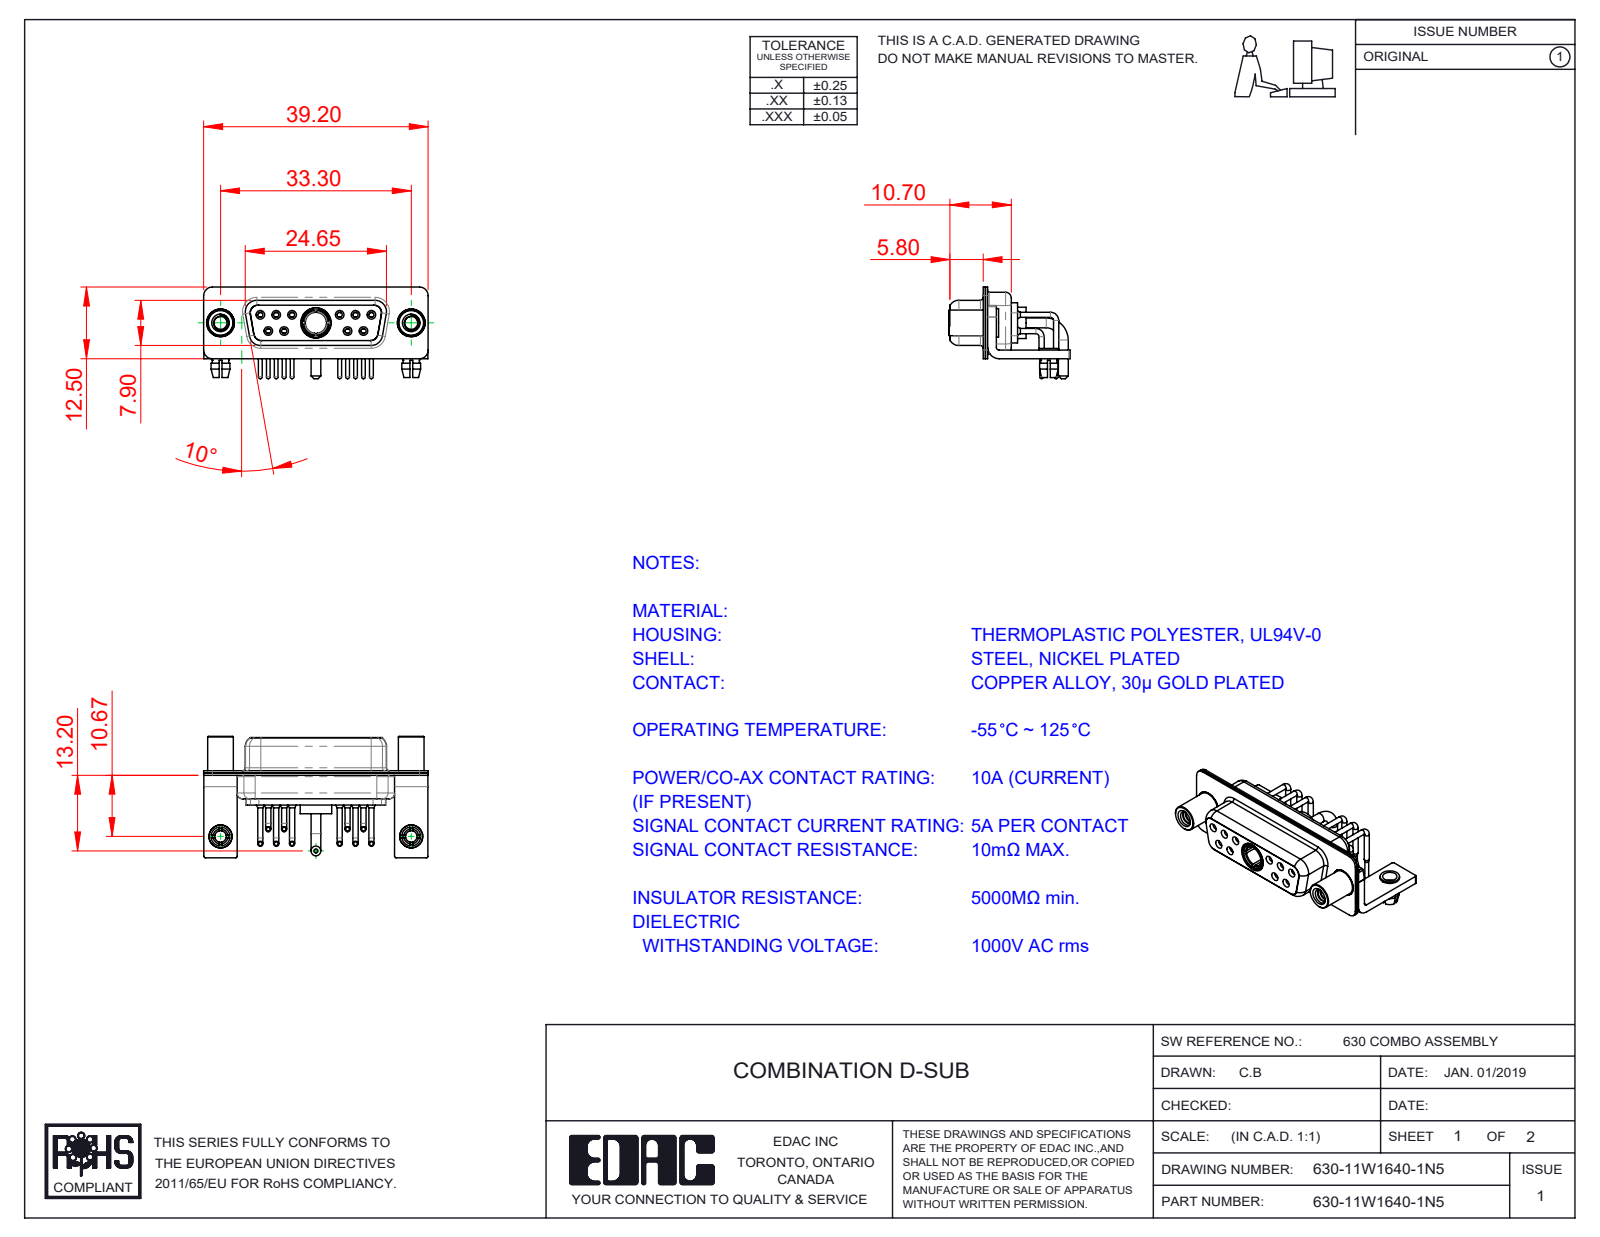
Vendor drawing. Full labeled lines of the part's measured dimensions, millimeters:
Part name (STEP PRODUCT): 630Combo Threaded Standoff_5; 630Combo Shell Front_15 Contacts; 630Combo Board Lock; Power Socket_10A RA (+6 more)
STEP written by: SolidWorks 2020 (CONFIG_CONTROL_DESIGN)
Units: millimetres
Bodies: 21 solids, 1067 faces (316 planar, 484 cylindrical, 267 other)
Overall size (bounding box): 39.2 × 21.2 × 16
Volume: 3 021 mm³ · Surface area: 7 346 mm²
Round holes (diameter × count): ⌀2 ×12, ⌀0.9 ×10, ⌀1.1 ×10, ⌀1.5 ×10, ⌀1.7 ×6, ⌀1.6 ×4, ⌀4.85 ×3, ⌀2.26 ×2, ⌀2.5 ×2, ⌀3.2 ×2, ⌀4 ×2, ⌀4.05 ×2
Round bosses / shafts (diameter × count): ⌀0.9 ×10, ⌀0.65 ×10, ⌀1.6 ×6, ⌀5 ×2, ⌀4.95 ×2, ⌀4.8 ×2, ⌀4.5 ×2, ⌀4 ×2
Partial cylindrical surfaces — rounded edges, fillets, slot ends (radius × count): R0.25 ×16, R1.5 ×16, R2 ×13, R1.35 ×12, R1.6 ×8, R0.5 ×5, R0.6 ×4, R0.65 ×4
Main face-to-face distances: 0.4, 0.8, 0.45, 1.4, 8.45, 1.5, 1.8, 8.9, 6.2, 2.3
Hole centre spacings: 3.16, 2.77, 13.85, 11.08, 16.62, 5.03, 5.04, 5.54
